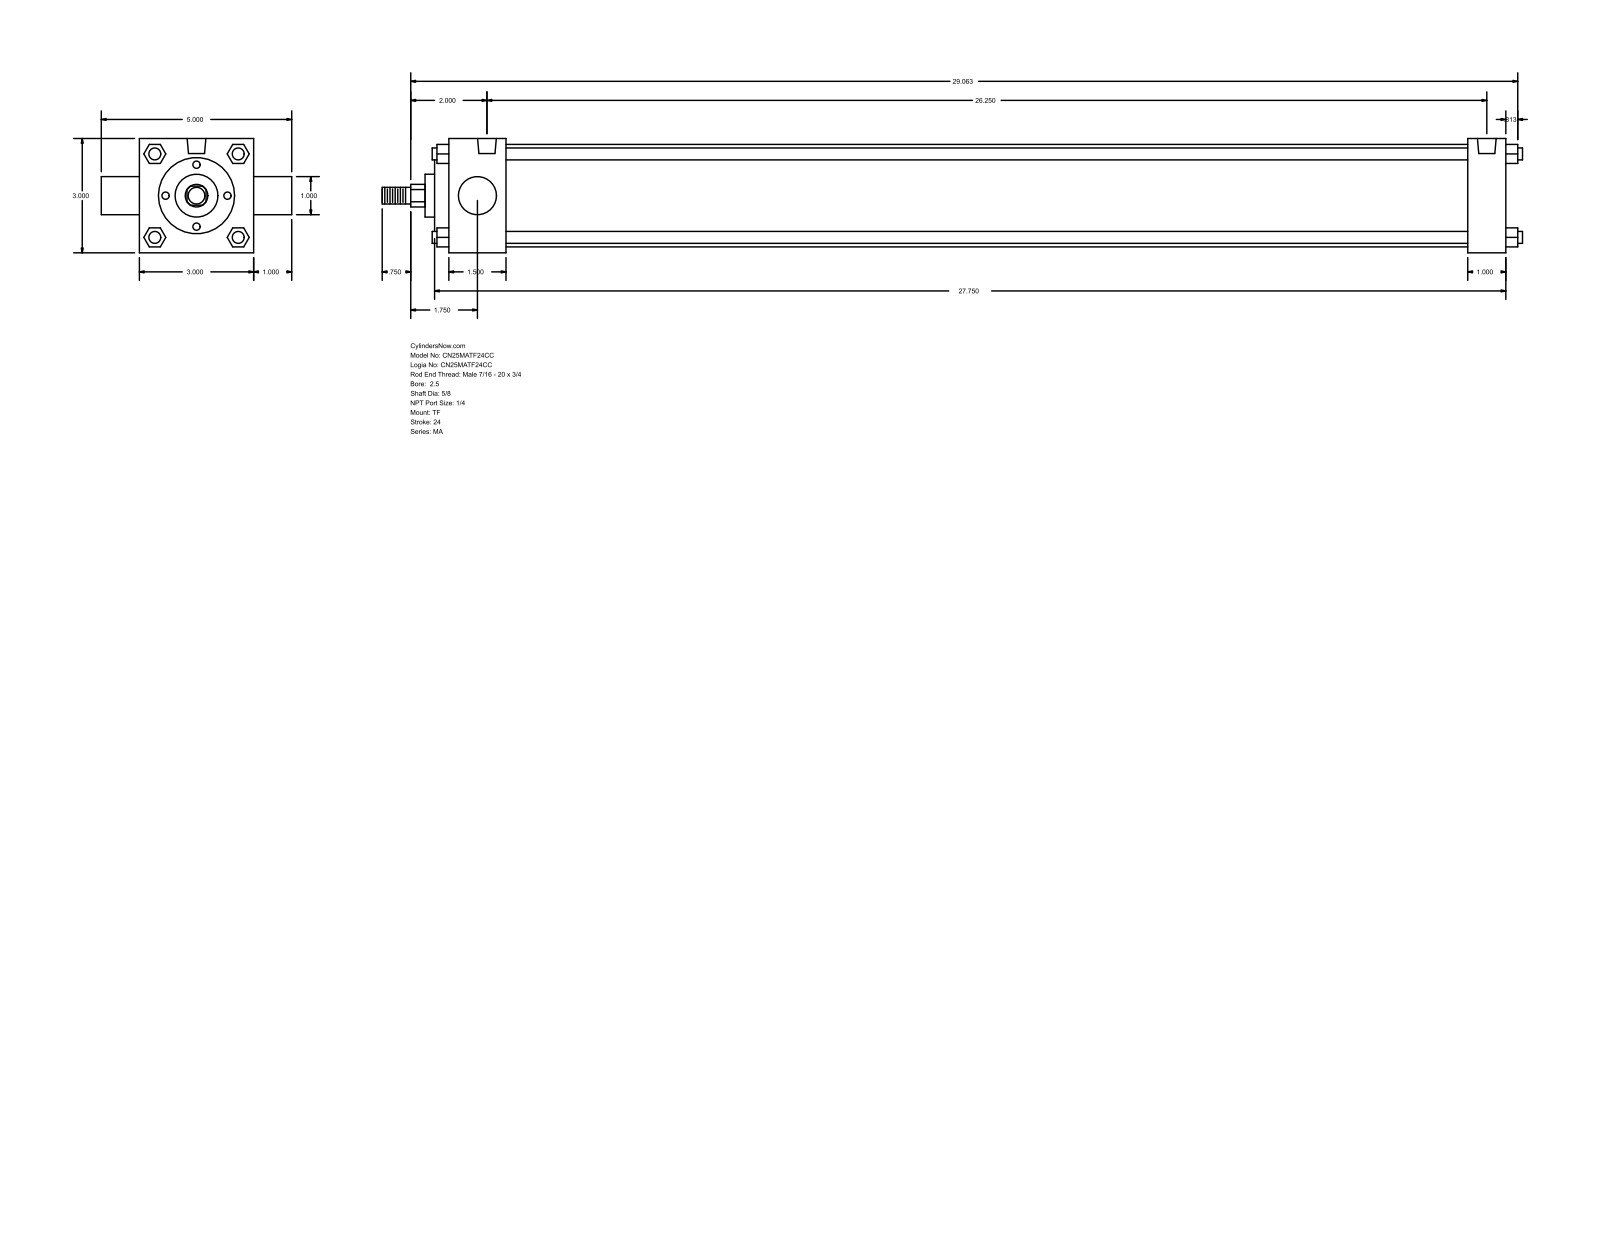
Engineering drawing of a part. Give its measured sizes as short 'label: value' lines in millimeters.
name: MA_TF__0250_0.625
written by: GSSL Pune (CONFIG_CONTROL_DESIGN)
unit: mm
bodies: 0 solids, 122 faces (93 planar, 29 cylindrical, 0 other)
size: 760.41 × 127 × 76.2
holes: 3× ⌀7.94, 2× ⌀12.49
bosses: 4× ⌀7.94, 1× ⌀68.33, 1× ⌀50.8, 1× ⌀28.57, 1× ⌀25.4, 1× ⌀15.88, 1× ⌀11.11
rounds: 1× R7.54
face distances: 76.2, 704.85, 25.4, 38.1, 679.45, 641.35, 666.75, 12.7, 9.52, 47.62
hole spacings: 666.75
